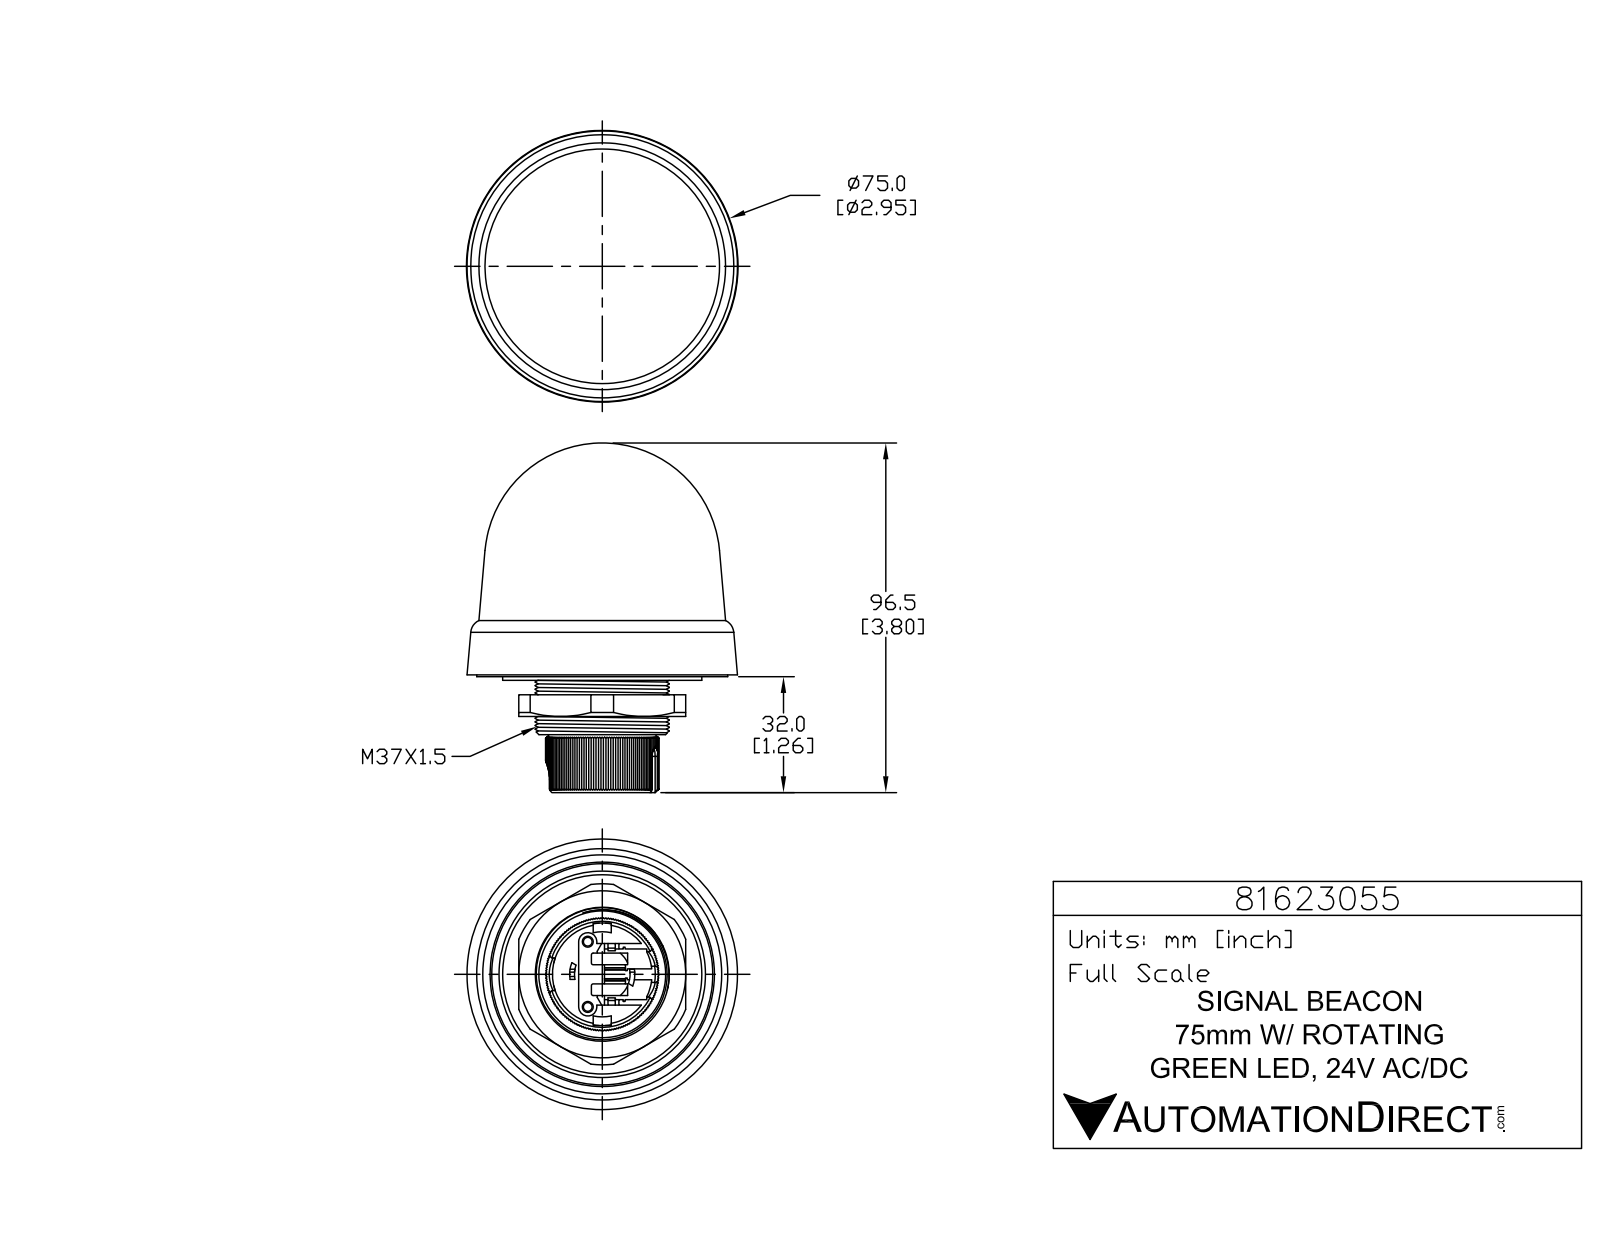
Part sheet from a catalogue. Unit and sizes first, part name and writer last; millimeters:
Units: millimetres
Overall size (bounding box): 96.5 × 74.7 × 74.7
Round holes (diameter × count): ⌀2.4 ×2, ⌀3 ×2, ⌀15.3 ×1, ⌀29 ×1
Round bosses / shafts (diameter × count): ⌀5.5 ×2, ⌀1.7 ×2, ⌀55 ×1, ⌀37 ×1, ⌀23.5 ×1
Partial cylindrical surfaces — rounded edges, fillets, slot ends (radius × count): R0.2 ×6, R1 ×6, R0.5 ×4, R0.8 ×2, R2 ×2, R2.5 ×2, R4.5 ×1, R9 ×1
Main face-to-face distances: 4.5, 9, 5, 11, 13, 8.5, 1.5, 10, 3, 4
Hole centre spacings: 9.9, 18
Volume: 202 500 mm³ · Surface area: 37 860 mm²
Bodies: 3 solids, 560 faces (432 planar, 80 cylindrical, 48 other)
Part name (STEP PRODUCT): 81623055
STEP written by: SolidWorks 2019 (CONFIG_CONTROL_DESIGN)
